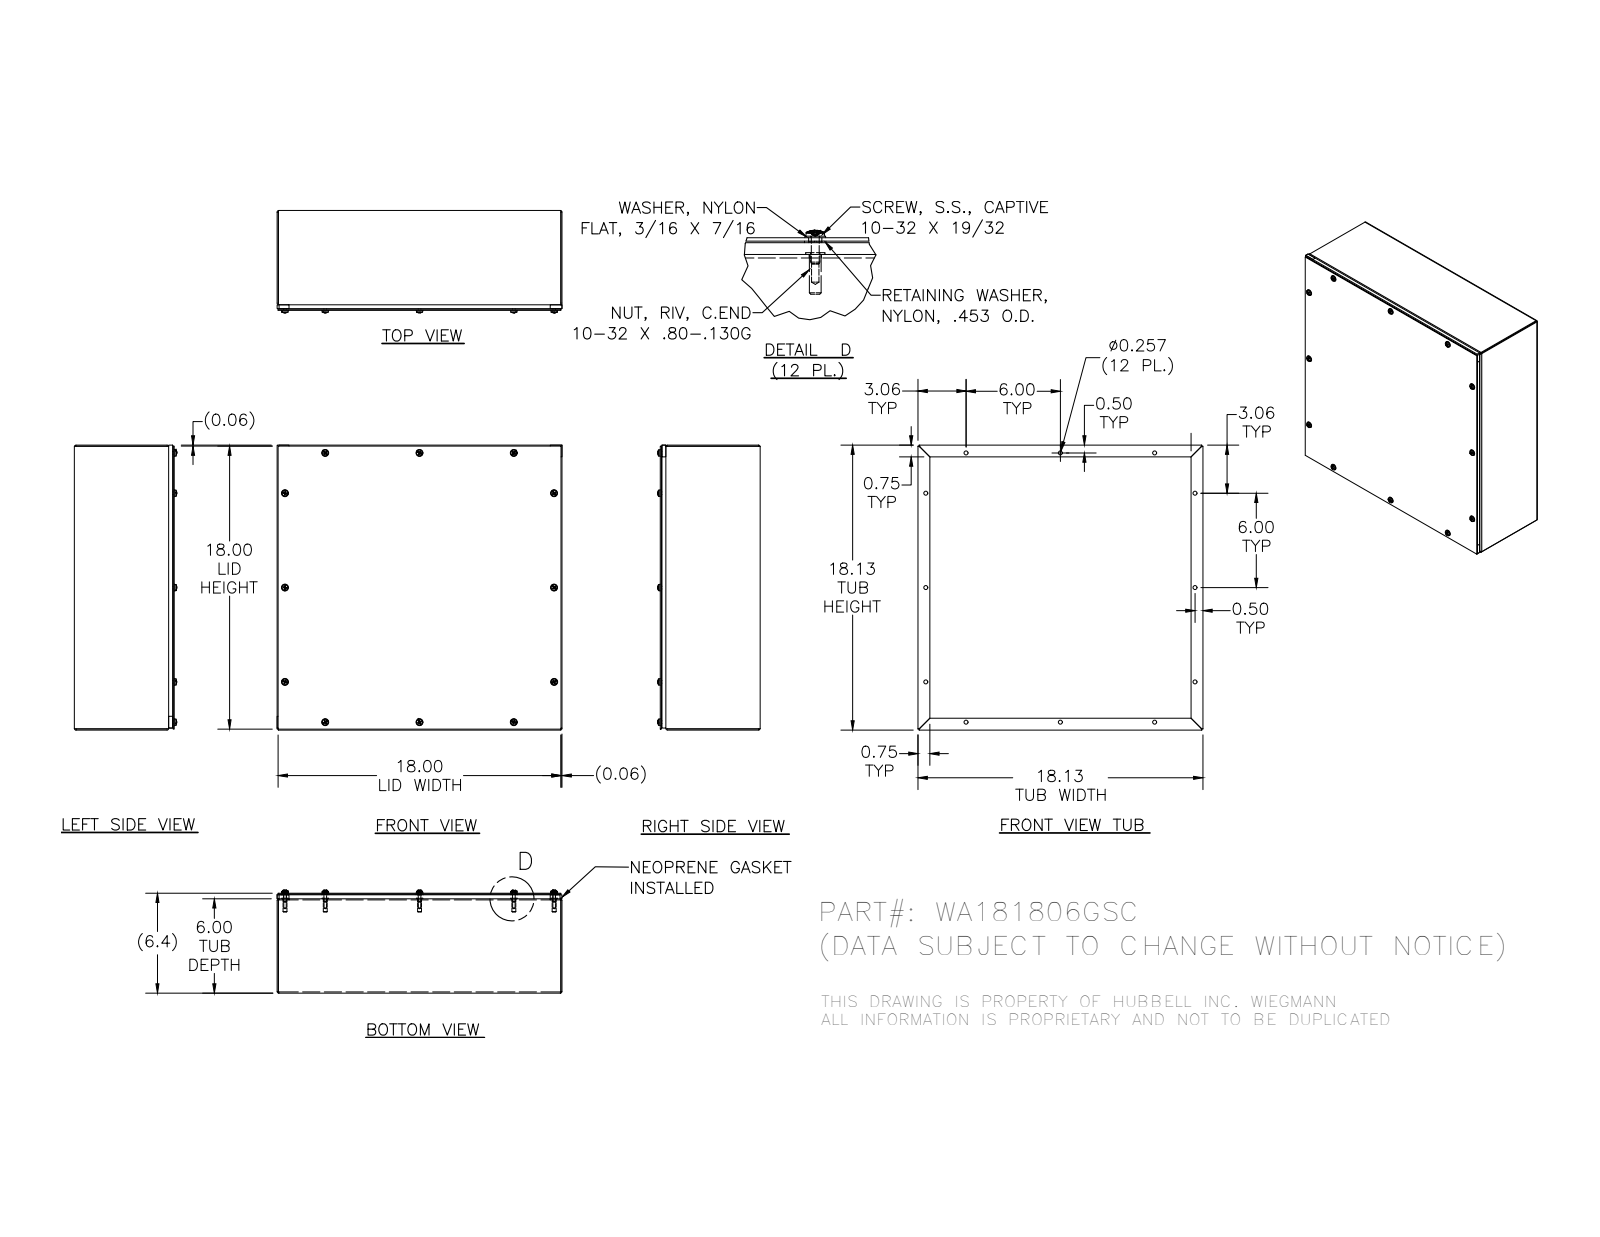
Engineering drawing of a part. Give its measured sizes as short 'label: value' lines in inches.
name: 39035; WA1818GSC_LP; WA181806GSC; WA181806GSCBKP (+3 more)
written by: SolidWorks 2014 (AUTOMOTIVE_DESIGN)
unit: in
bodies: 53 solids, 1258 faces (590 planar, 328 cylindrical, 340 other)
size: 18.125 × 18.125 × 6.511
volume: 93.73 in³; area: 2 396 in²
holes: 12× ⌀0.188, 12× ⌀0.257, 12× ⌀0.278, 12× ⌀0.281, 11× ⌀0.156, 11× ⌀0.196
bosses: 12× ⌀0.453, 12× ⌀0.437, 12× ⌀0.167, 11× ⌀0.406, 11× ⌀0.248
rounds: 12× R0.089, 8× R0.031, 8× R0.105
face distances: 0.074, 6.282, 18.051, 6.356, 6.208, 18.125, 17.977, 0.356, 5.926, 0.282
hole spacings: 6, 8.938, 18.146, 14.786, 12, 16.893, 16.893, 8.937
